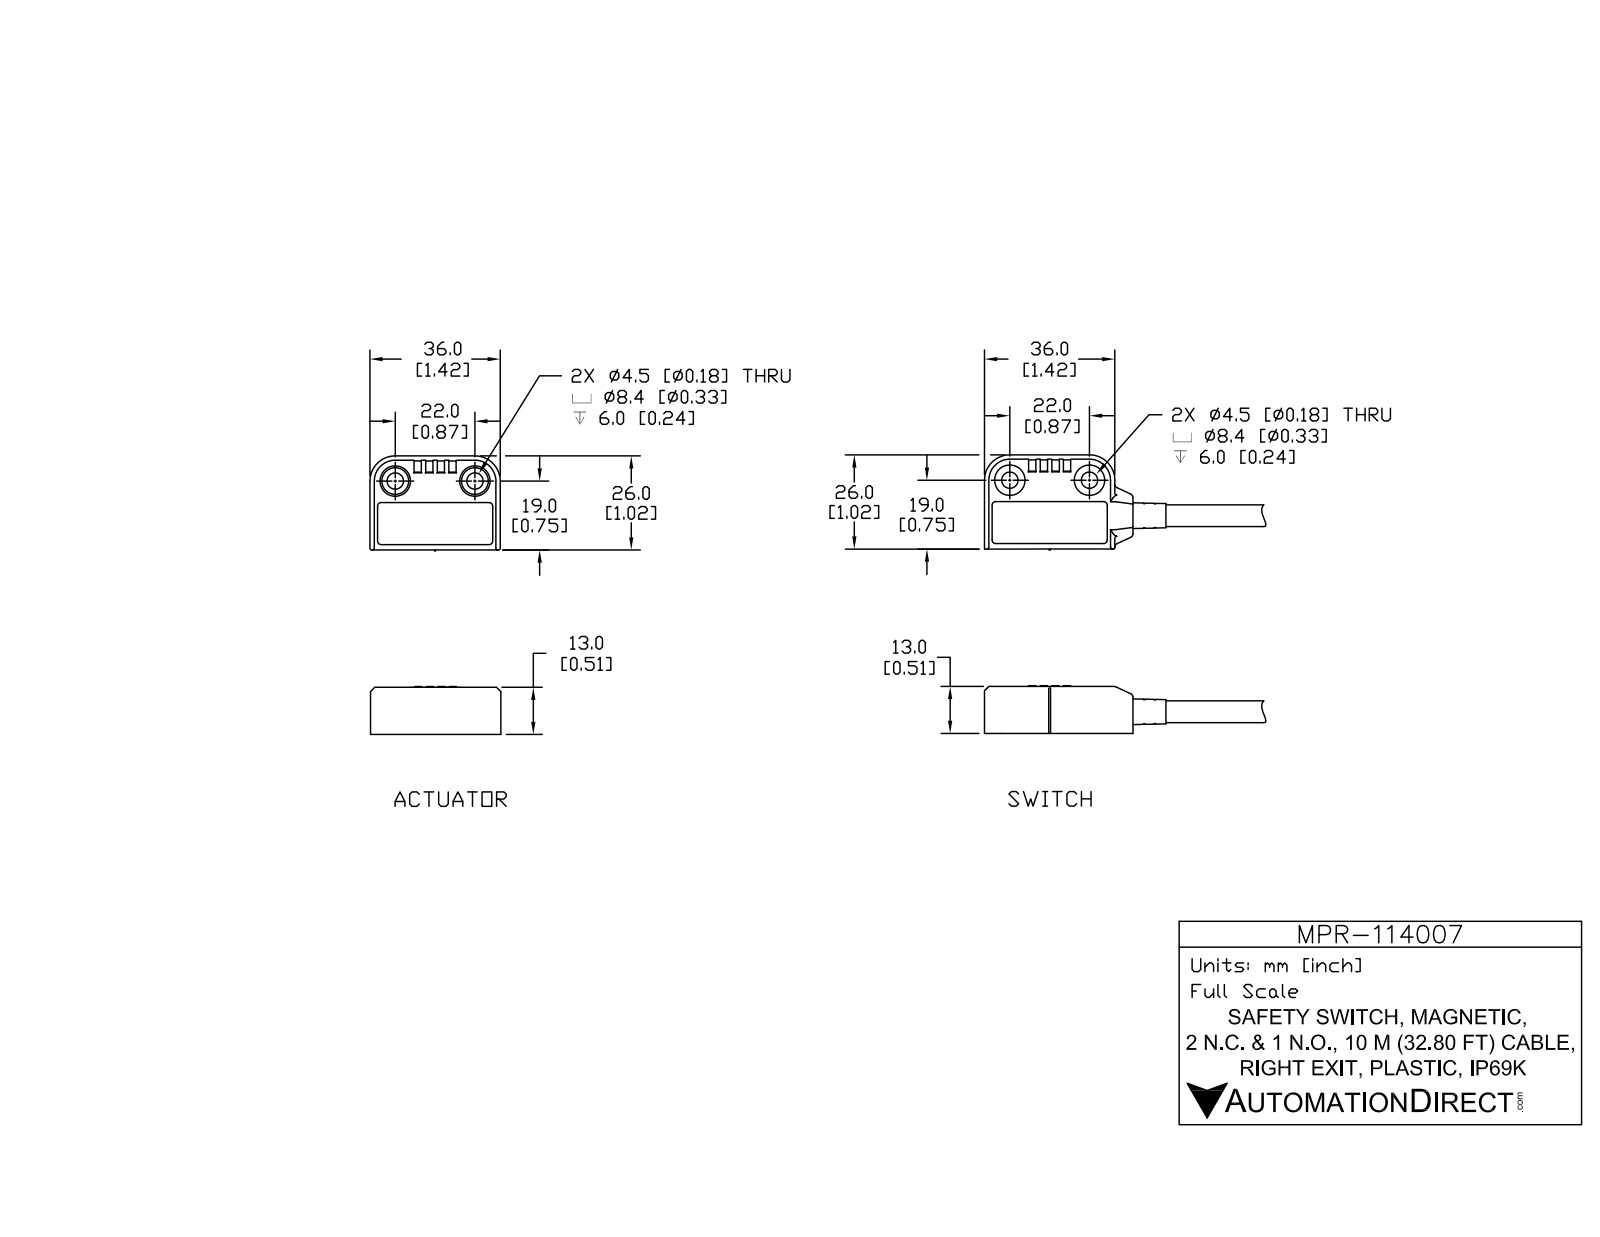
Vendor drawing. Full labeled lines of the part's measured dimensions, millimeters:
Part name (STEP PRODUCT): MPR-114007; MPR-114007_1; MPR-114007_2
STEP written by: SolidWorks 2017 (AUTOMOTIVE_DESIGN)
Units: millimetres
Bodies: 9 solids, 1110 faces (486 planar, 325 cylindrical, 299 other)
Overall size (bounding box): 194.5 × 53 × 13.4
Volume: 17 350 mm³ · Surface area: 19 080 mm²
Round holes (diameter × count): ⌀4.5 ×4, ⌀8.4 ×4, ⌀5 ×2, ⌀5 ×1, ⌀5.9 ×1, ⌀7 ×1
Round bosses / shafts (diameter × count): ⌀2 ×3, ⌀5 ×2, ⌀2.3 ×2, ⌀8.6 ×1, ⌀7.6 ×1, ⌀7.1 ×1, ⌀6 ×1
Partial cylindrical surfaces — rounded edges, fillets, slot ends (radius × count): R0.5 ×85, R0.2 ×30, R0.3 ×28, R0.1 ×17, R1 ×13, R4.3 ×4, R5.1 ×4, R7 ×4
Main face-to-face distances: 1.4, 11.7, 9.9, 11.5, 1.2, 27, 1.5, 2.4, 11.3, 0.8
Hole centre spacings: 22, 11.3, 24.7, 27.7, 35.4, 39, 44.8, 10.1
